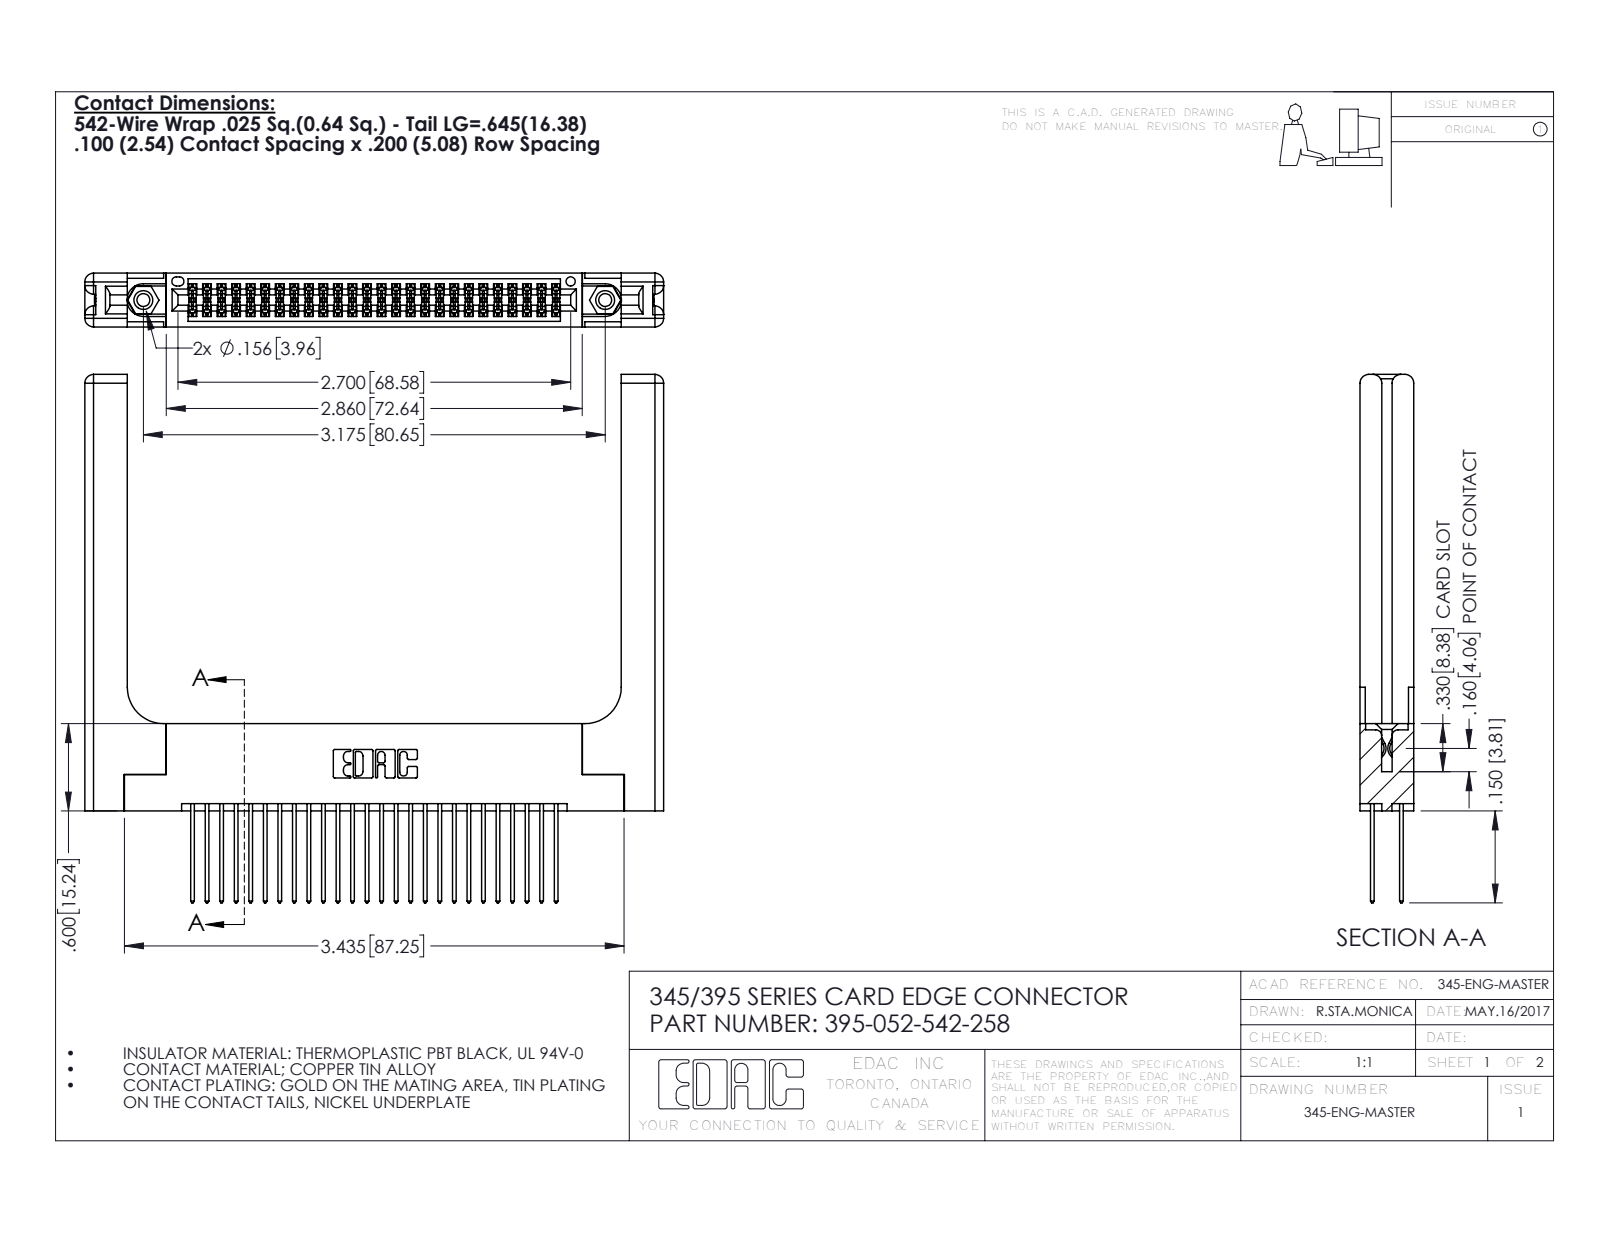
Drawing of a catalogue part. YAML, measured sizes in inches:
part_name: "345 Part_Flush Mounting Lugs - 0.156 Dia-TH; 345-220-058_345-220-058; 395-052-542-258; 345-250-001_345-250-001-102 (+1 more)"
step_written_by: "SolidWorks 2016 (CONFIG_CONTROL_DESIGN)"
units: inches
bodies: {solids: 57, faces: 2982, planar: 1944, cylindrical: 978, other: 60}
overall_size: [3.979, 3.632, 0.37]
volume: 1.122
surface_area: 31.83
round_holes:
  - {diameter: 0.089, count: 2}
  - {diameter: 0.125, count: 2}
  - {diameter: 0.156, count: 2}
  - {diameter: 0.064, count: 1}
round_bosses_or_shafts:
  - {diameter: 0.155, count: 2}
partial_cylinders:
  - {radius: 0.006, count: 78}
  - {radius: 0.01, count: 52}
  - {radius: 0.01, count: 22}
  - {radius: 0.06, count: 16}
  - {radius: 0.007, count: 6}
  - {radius: 0.031, count: 6}
  - {radius: 0.026, count: 3}
  - {radius: 0.014, count: 2}
face_to_face_distances: [0.072, 0.298, 0.37, 0.2, 0.098, 0.272, 0.025, 0.225, 0.148, 0.15]
hole_center_spacings: [0.27, 2.94, 3.175]
